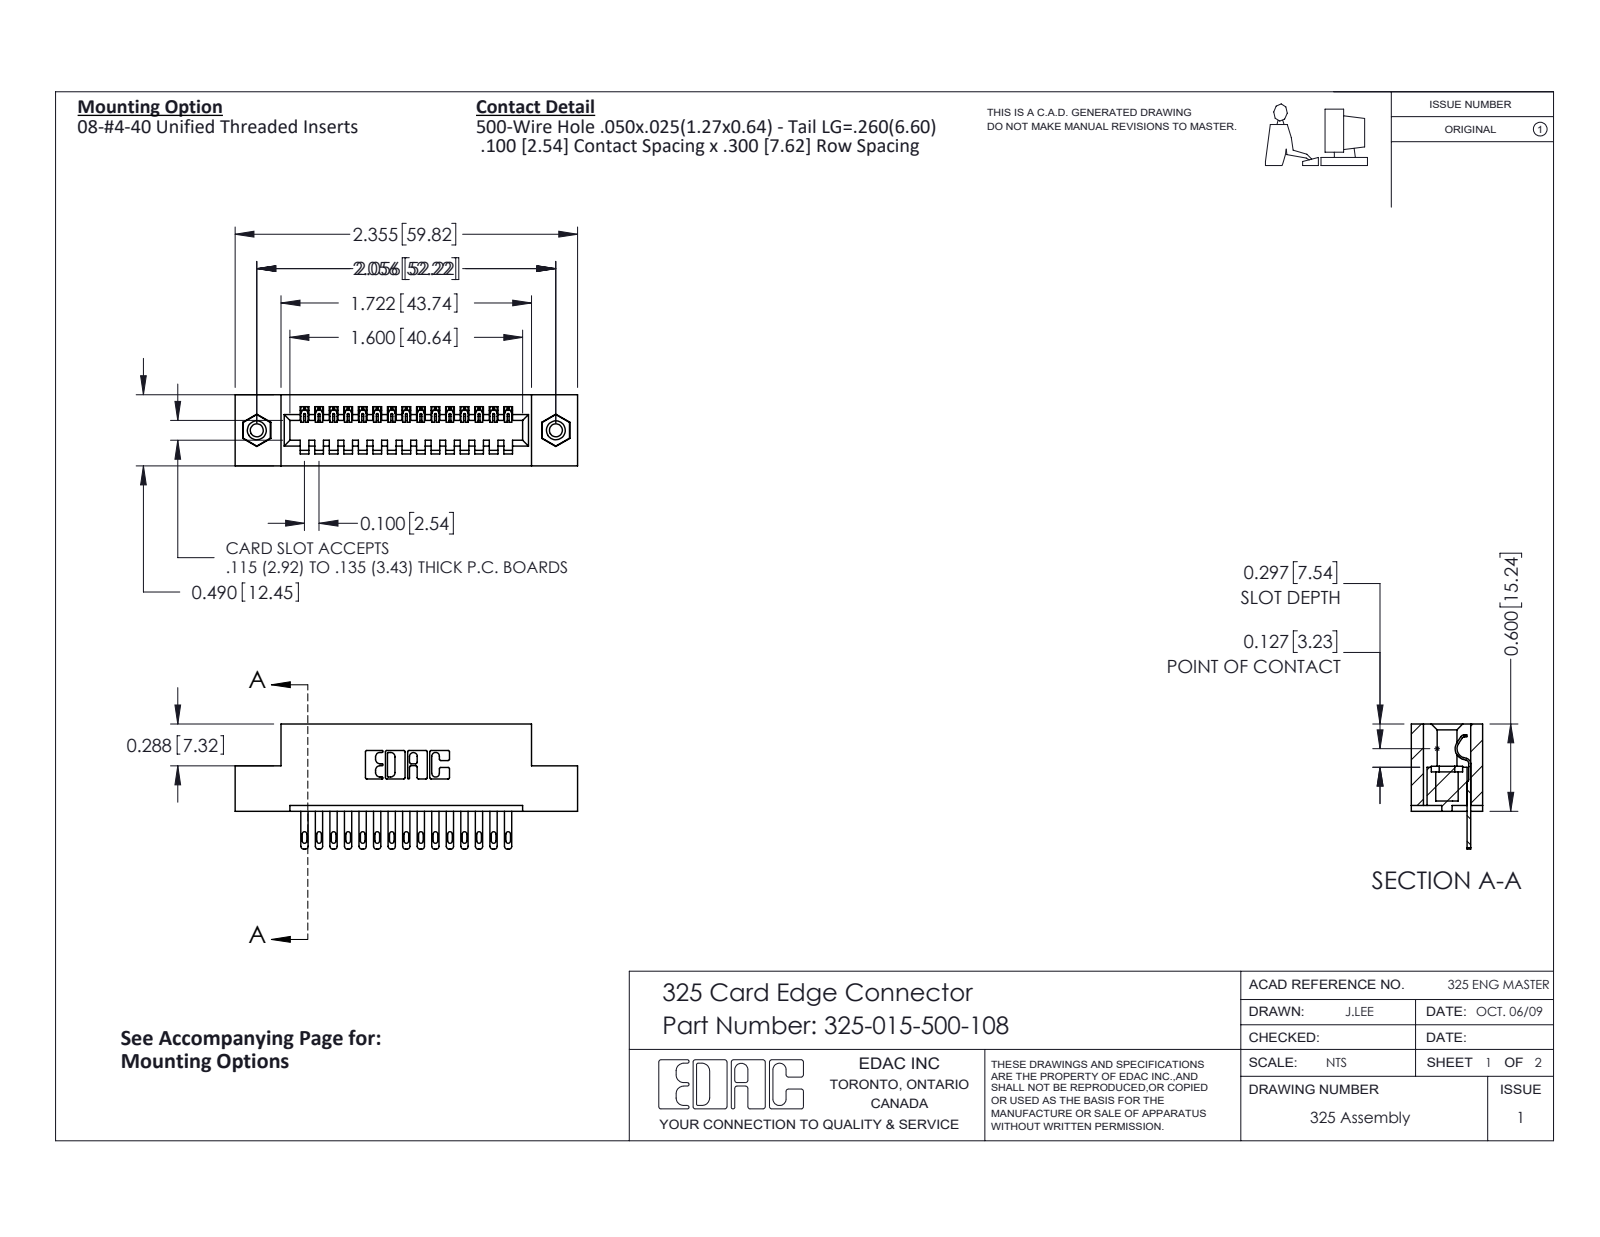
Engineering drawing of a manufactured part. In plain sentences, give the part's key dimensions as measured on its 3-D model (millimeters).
The part is named "325-292-001_325-293-100; 325 Part_TI; 325-015-500-108; 345-250-001_345-250-003-102". Its 3-D file was written by "SolidWorks 2016 (CONFIG_CONTROL_DESIGN)". It is 18 solids with 984 faces: 642 planar, 326 cylindrical and 16 other. Overall it measures 59.8 by 21.8 by 12.4 millimeters. Its volume is 7 390 cubic millimeters and its surface area 7 658 square millimeters. Round holes: 2 of diameter 2.3, 2 of diameter 3.2, 2 of diameter 4.1. Round bosses or shafts: 2 of diameter 3.9. Partial cylindrical surfaces (rounded edges, fillets, slot ends): 30 of radius 0.2, 30 of radius 0.4, 30 of radius 0.5, 22 of radius 0.3, 6 of radius 0.2, 6 of radius 0.8, 3 of radius 0.7, 1 of radius 0.4. The main face-to-face distances are 2.1, 10.3, 7.6, 12.4, 2.7, 9.7, 0.6, 1, 2.5, 15.2. The hole center spacings are 52.2.
